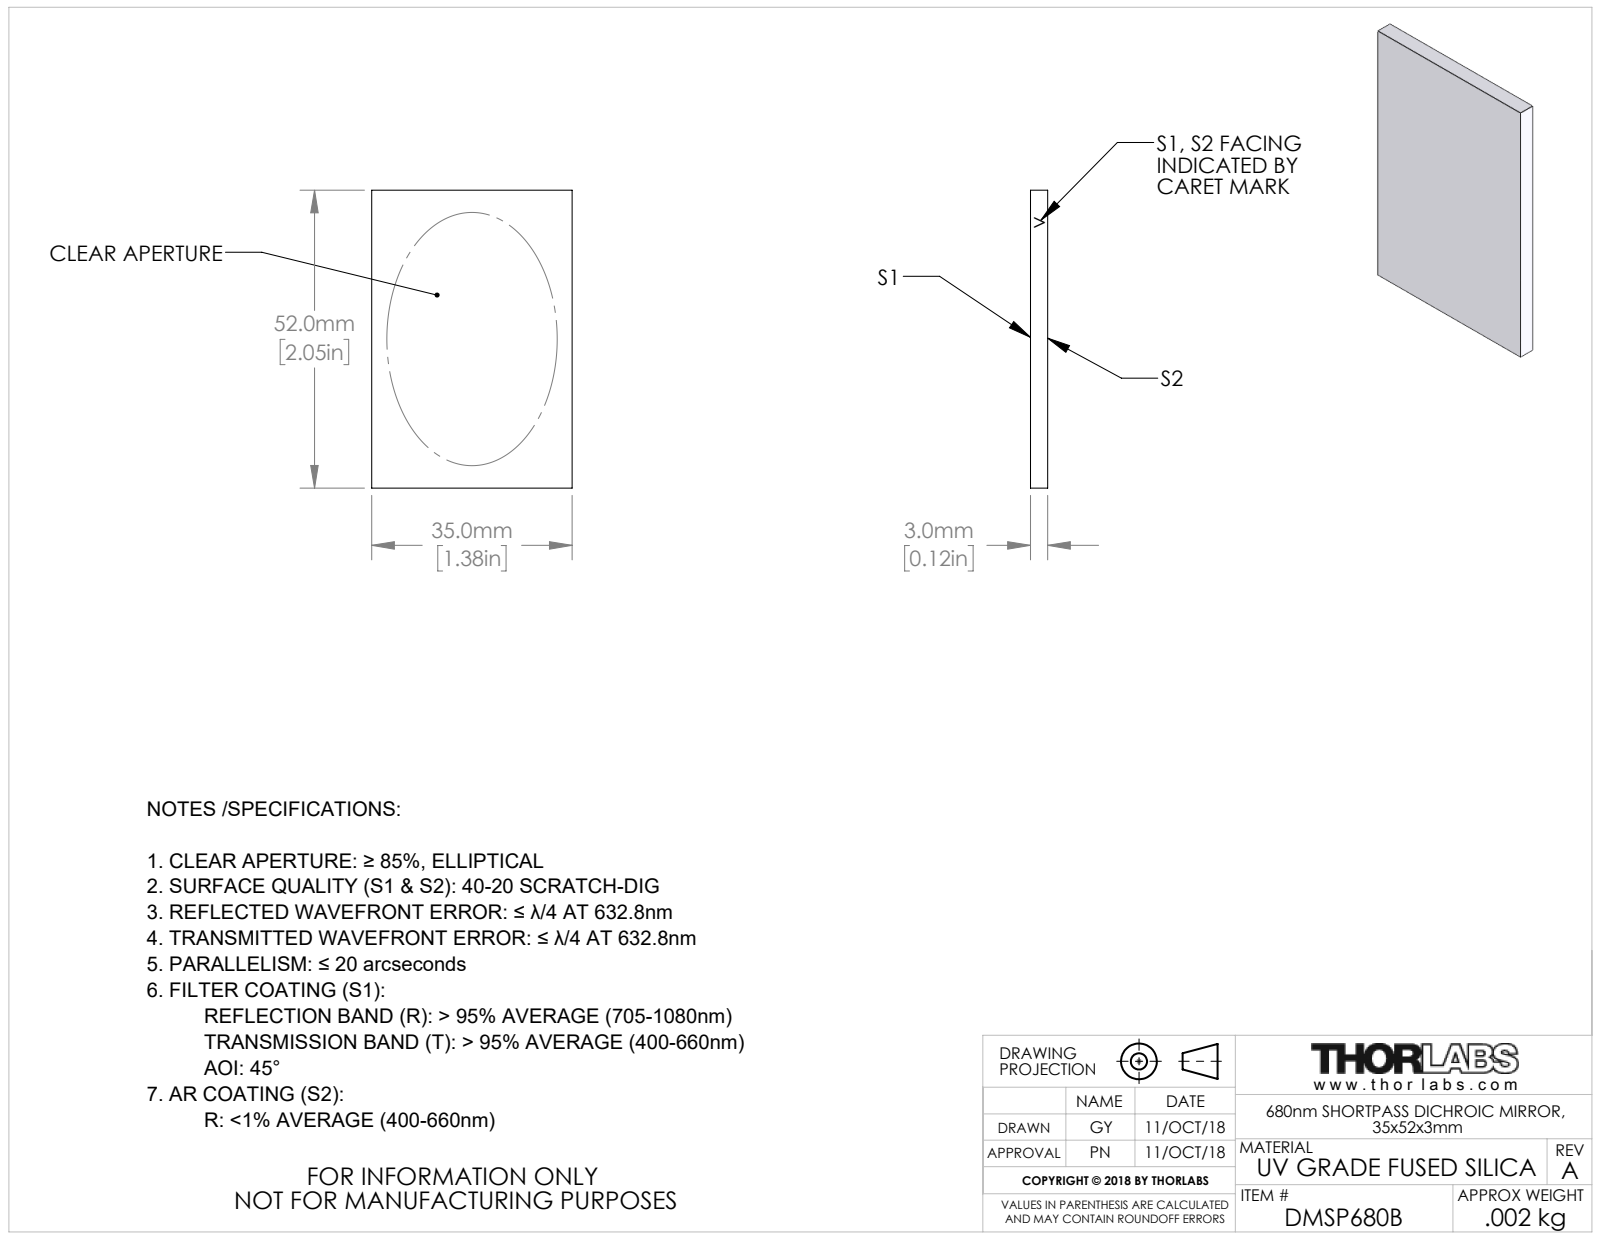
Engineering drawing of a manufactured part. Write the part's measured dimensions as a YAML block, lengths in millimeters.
part_name: "TTN166723-E0W"
step_written_by: "SolidWorks 2018 (AUTOMOTIVE_DESIGN)"
units: millimeters
bodies: {solids: 1, faces: 6, planar: 6, cylindrical: 0, other: 0}
overall_size: [52, 35, 3]
volume: 5460
surface_area: 4162
face_to_face_distances: [3, 35, 52]
